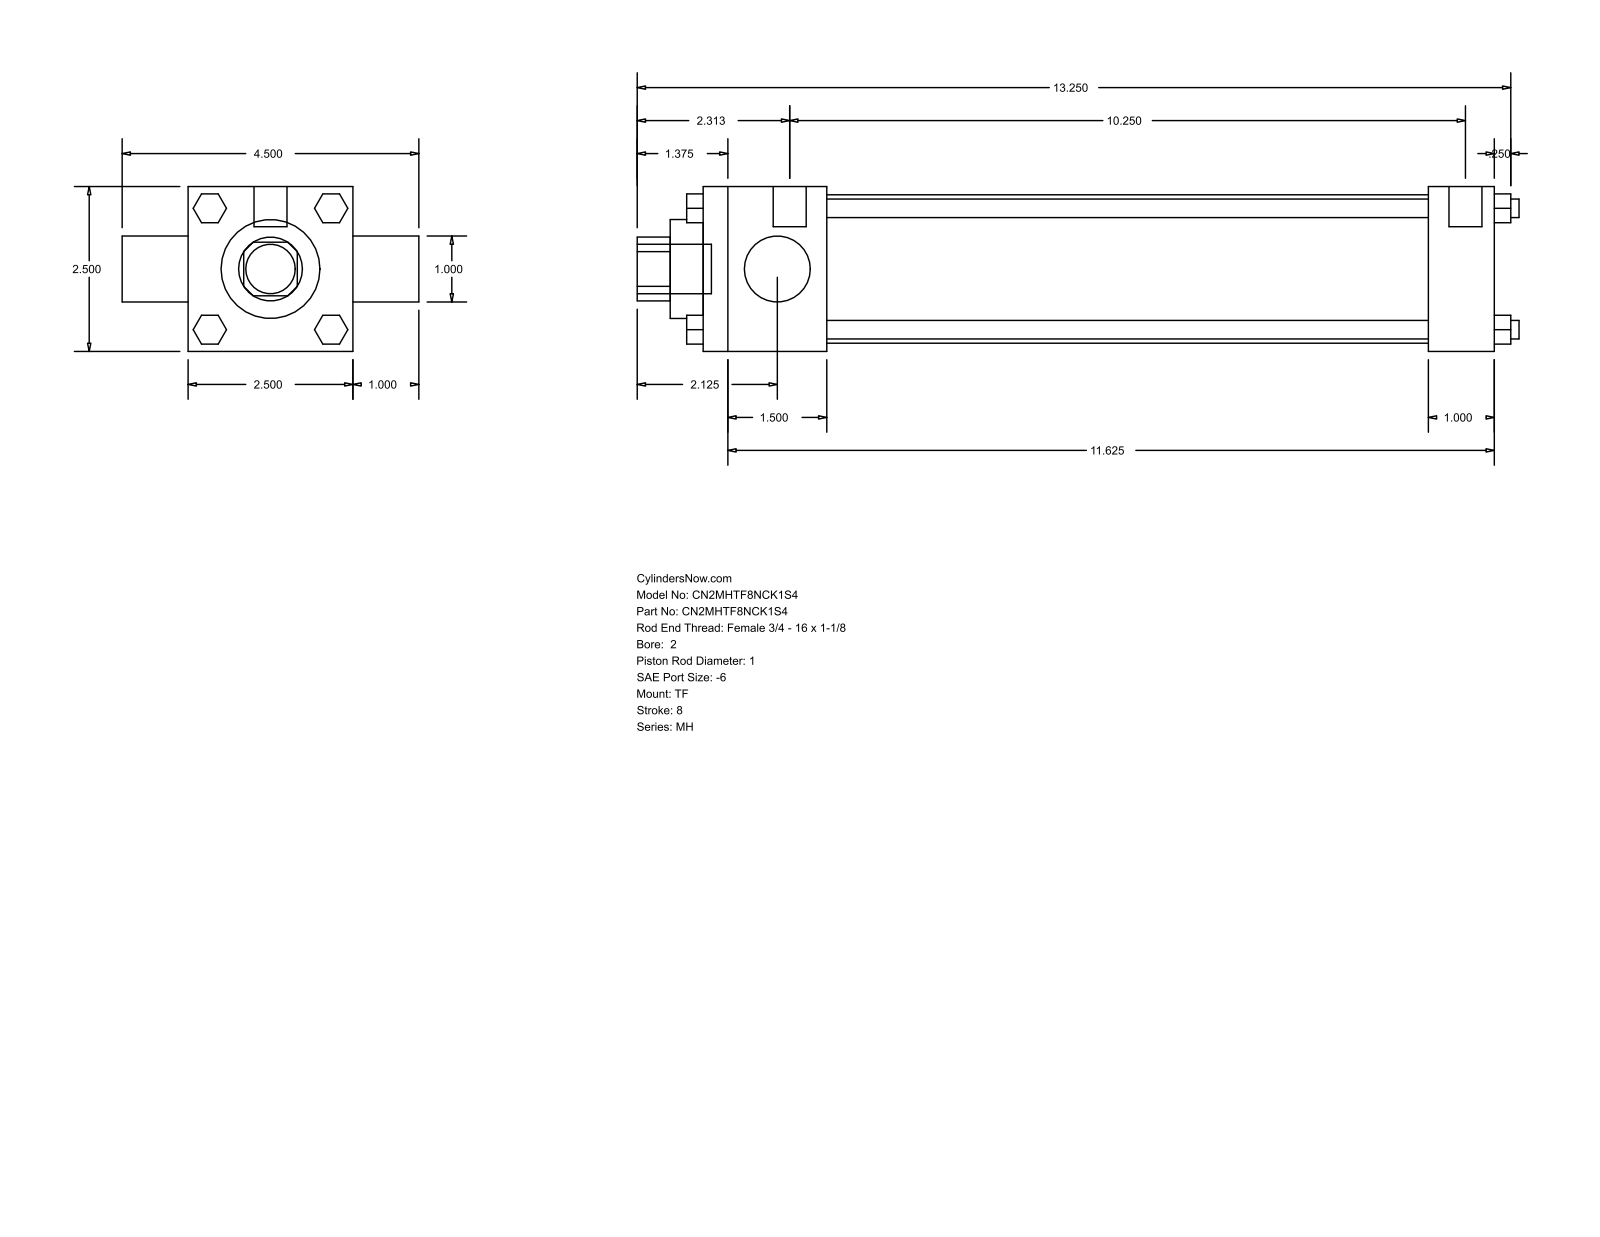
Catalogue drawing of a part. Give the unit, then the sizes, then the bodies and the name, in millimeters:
Units: millimetres
Overall size (bounding box): 339.73 × 114.3 × 63.5
Round holes (diameter × count): ⌀25.4 ×2, ⌀38.1 ×1, ⌀57.15 ×1
Round bosses / shafts (diameter × count): ⌀7.14 ×4, ⌀5.56 ×3, ⌀12.7 ×2, ⌀19.05 ×1
Partial cylindrical surfaces — rounded edges, fillets, slot ends (radius × count): R12.29 ×1
Main face-to-face distances: 63.5, 304.8, 25.4, 47.63, 279.4, 231.77, 257.17, 88.9, 317.5, 6.35
Bodies: 0 solids, 120 faces (92 planar, 28 cylindrical, 0 other)
Part name (STEP PRODUCT): MH_TF__0200_1
STEP written by: GSSL Pune (CONFIG_CONTROL_DESIGN)
